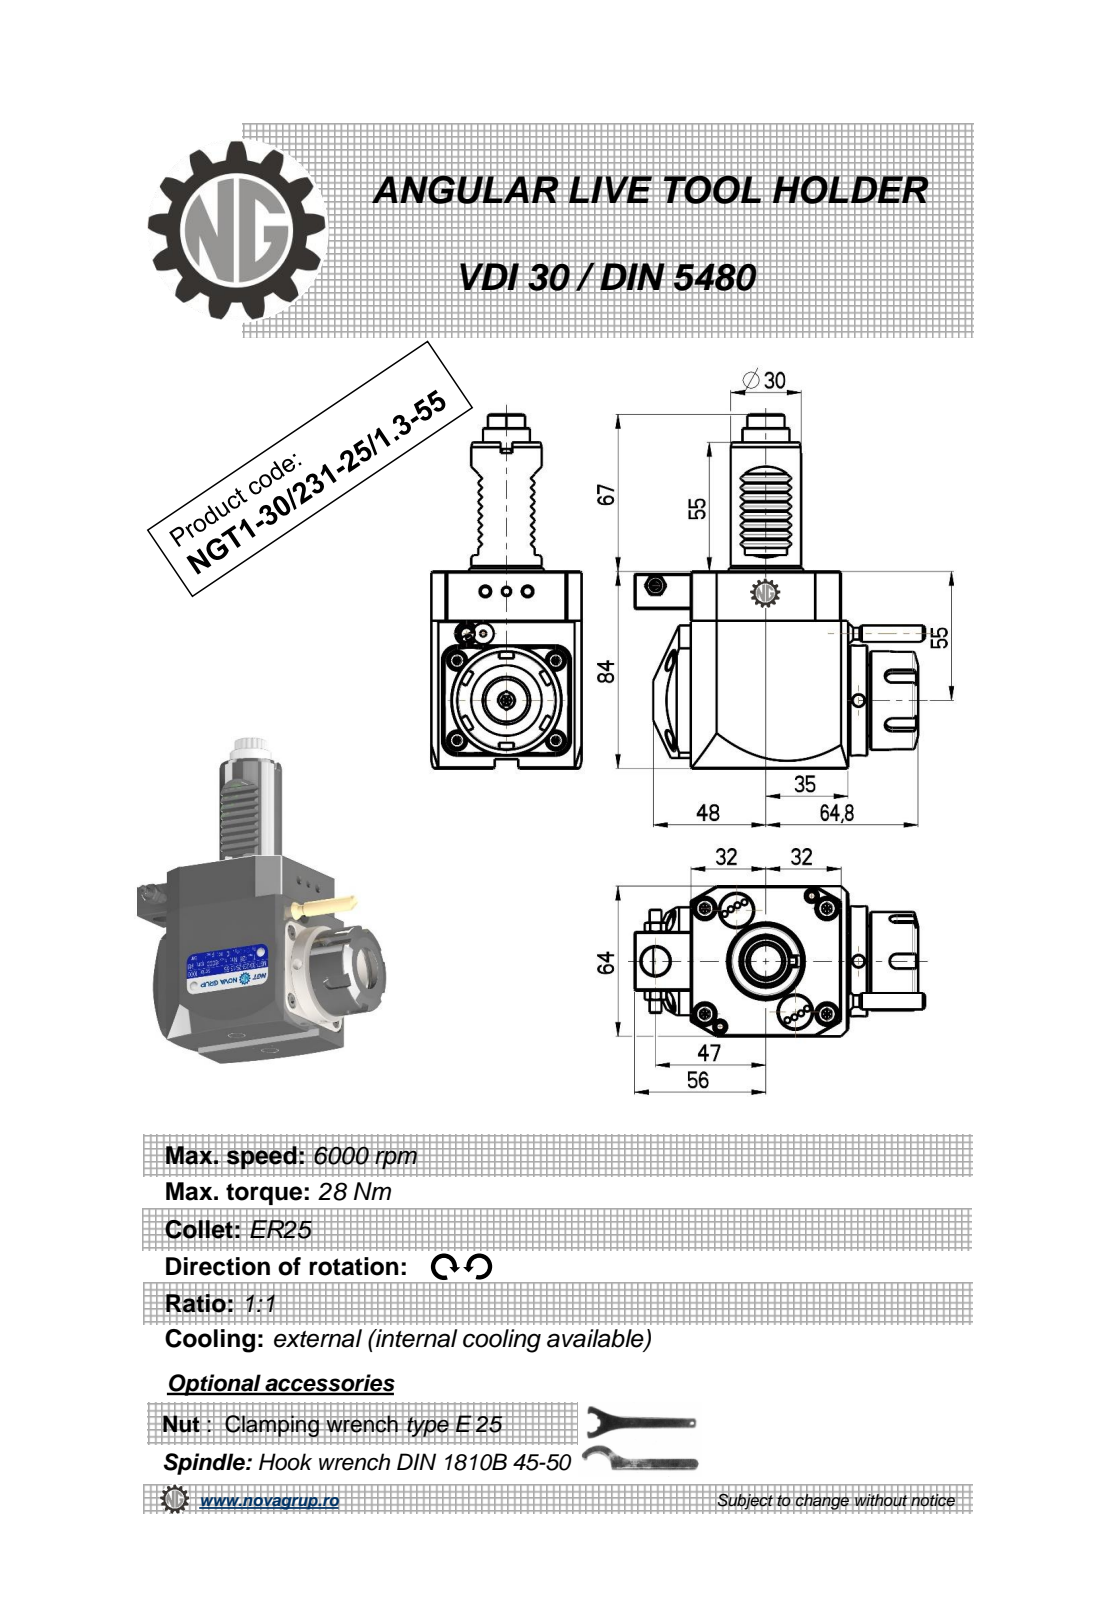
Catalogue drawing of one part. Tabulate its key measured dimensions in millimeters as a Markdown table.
| quantity | value |
| --- | --- |
| part name | NGT1_30_231_25_1_3_55 |
| STEP written by | PRO/ENGINEER BY PARAMETRIC TECHNOLOGY CORPORATION, 2010280 (CONFIG_CONTROL_DESIGN) |
| units | millimeters |
| bodies | 1 solid, 562 faces (227 planar, 165 cylindrical, 170 other) |
| overall size | 151 × 123.83 × 64 |
| volume | 456 709 mm³ |
| surface area | 48 180 mm² |
| round holes (diameter × count) | 5 × 2, 2.5 × 1, 3 × 1, 4.2 × 1, 9.5 × 1, 12 × 1, 20.3 × 1 |
| round bosses / shafts (diameter × count) | 8.96 × 2, 5 × 2, 47 × 1, 42 × 1, 35 × 1, 30 × 1, 20 × 1, 7 × 1 |
| partial cylindrical surfaces (radius × count) | 1.98 × 36, 0.3 × 16, 0.26 × 12, 3 × 5, 3.5 × 4, 160 × 2, 7.08 × 1, 7.92 × 1 |
| main face-to-face distances | 64, 84, 0.5, 67.2, 67, 7.5, 8, 83, 3, 3.2 |
| hole center spacings | 24.76, 33.19, 46.5, 86.45, 99.37 |
